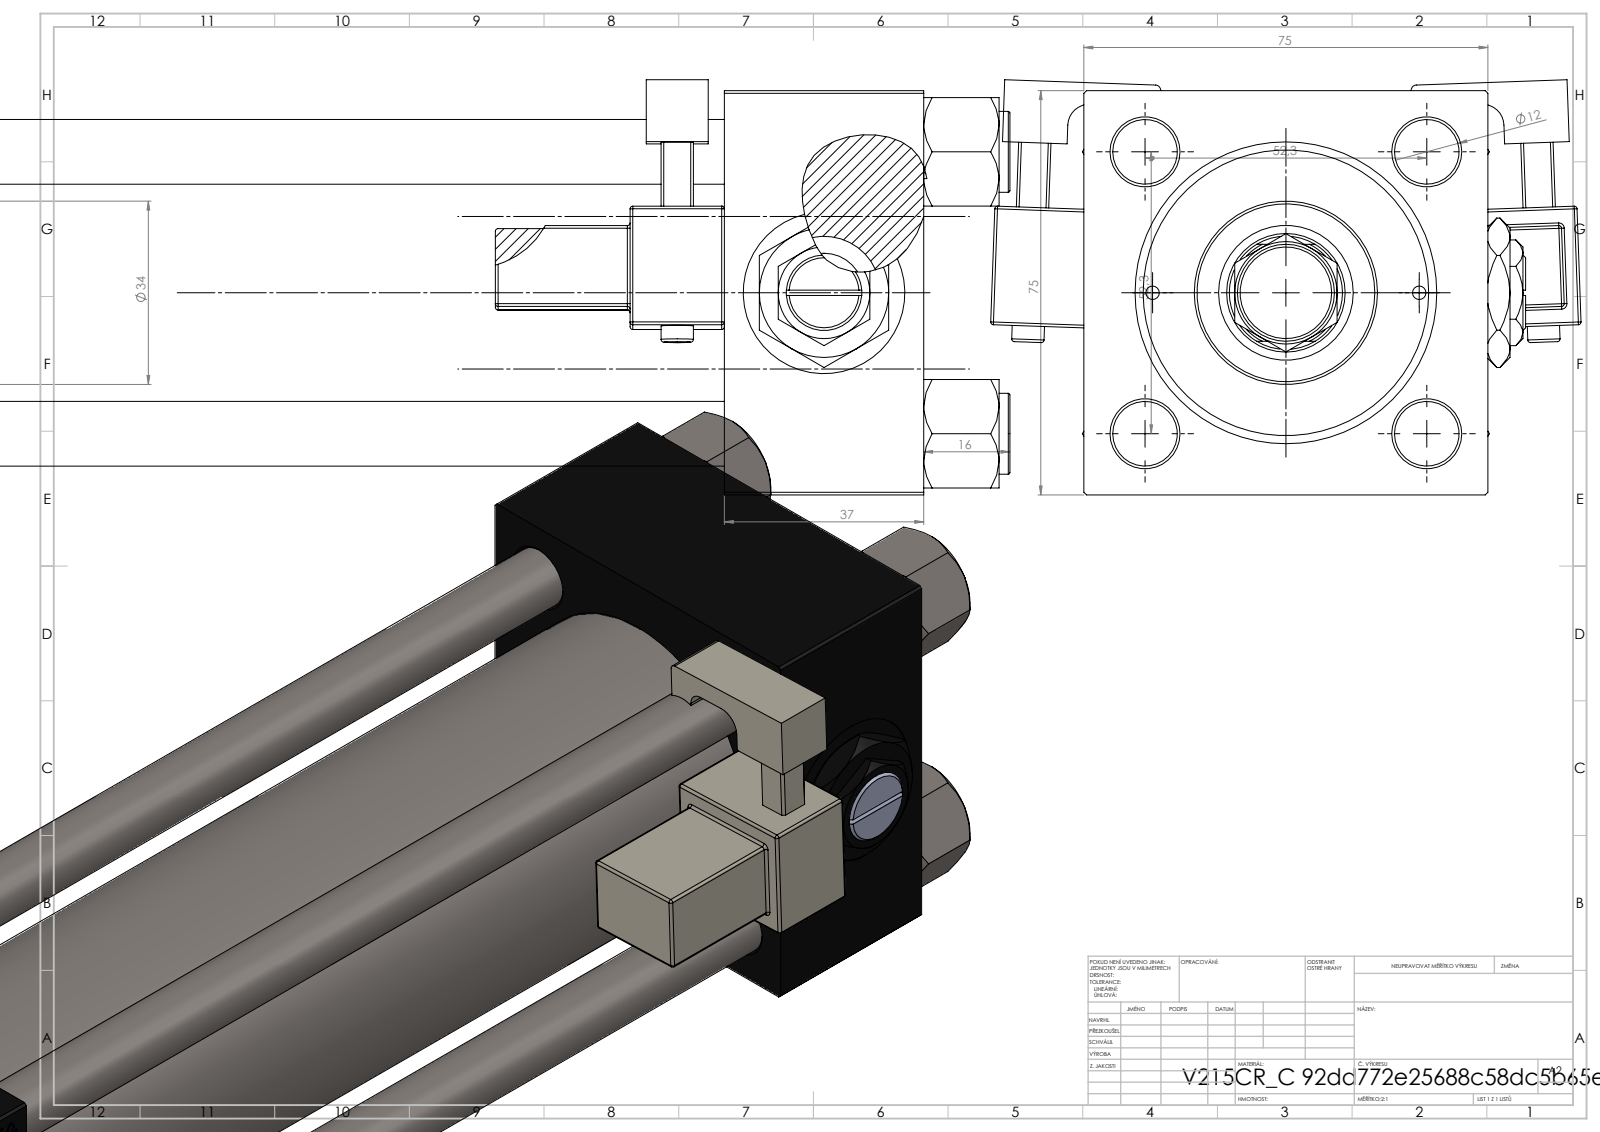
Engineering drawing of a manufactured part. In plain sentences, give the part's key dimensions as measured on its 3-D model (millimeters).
The part is named "V215CR_C_Body; NUT_M5_C; Zatka_pro_OIL_PORT; MFA (+4 more)". Its 3-D file was written by "SolidWorks 2019 (CONFIG_CONTROL_DESIGN)". It is 16 solids with 1461 faces: 649 planar, 166 cylindrical and 646 other. Overall it measures 368 by 109.57 by 77.03 millimeters. Its volume is 887 488 cubic millimeters and its surface area 244 216 square millimeters. Round holes: 4 of diameter 12, 2 of diameter 2.5, 2 of diameter 7, 2 of diameter 20.96, 2 of diameter 30, 1 of diameter 10.5, 1 of diameter 22, 1 of diameter 25, 1 of diameter 41, 1 of diameter 50, 1 of diameter 53. Round bosses or shafts: 4 of diameter 15, 2 of diameter 6, 1 of diameter 56, 1 of diameter 34, 1 of diameter 18, 1 of diameter 11. Partial cylindrical surfaces (rounded edges, fillets, slot ends): 48 of radius 0.5, 2 of radius 1, 2 of radius 2.5, 2 of radius 4, 1 of radius 10.5. The main face-to-face distances are 75, 37, 294, 257, 235, 198, 59, 265.3, 228.3, 30.3. The hole center spacings are 26.19, 36.98, 52.3, 57.22, 24.75, 73.96, 49.5, 233.5.
